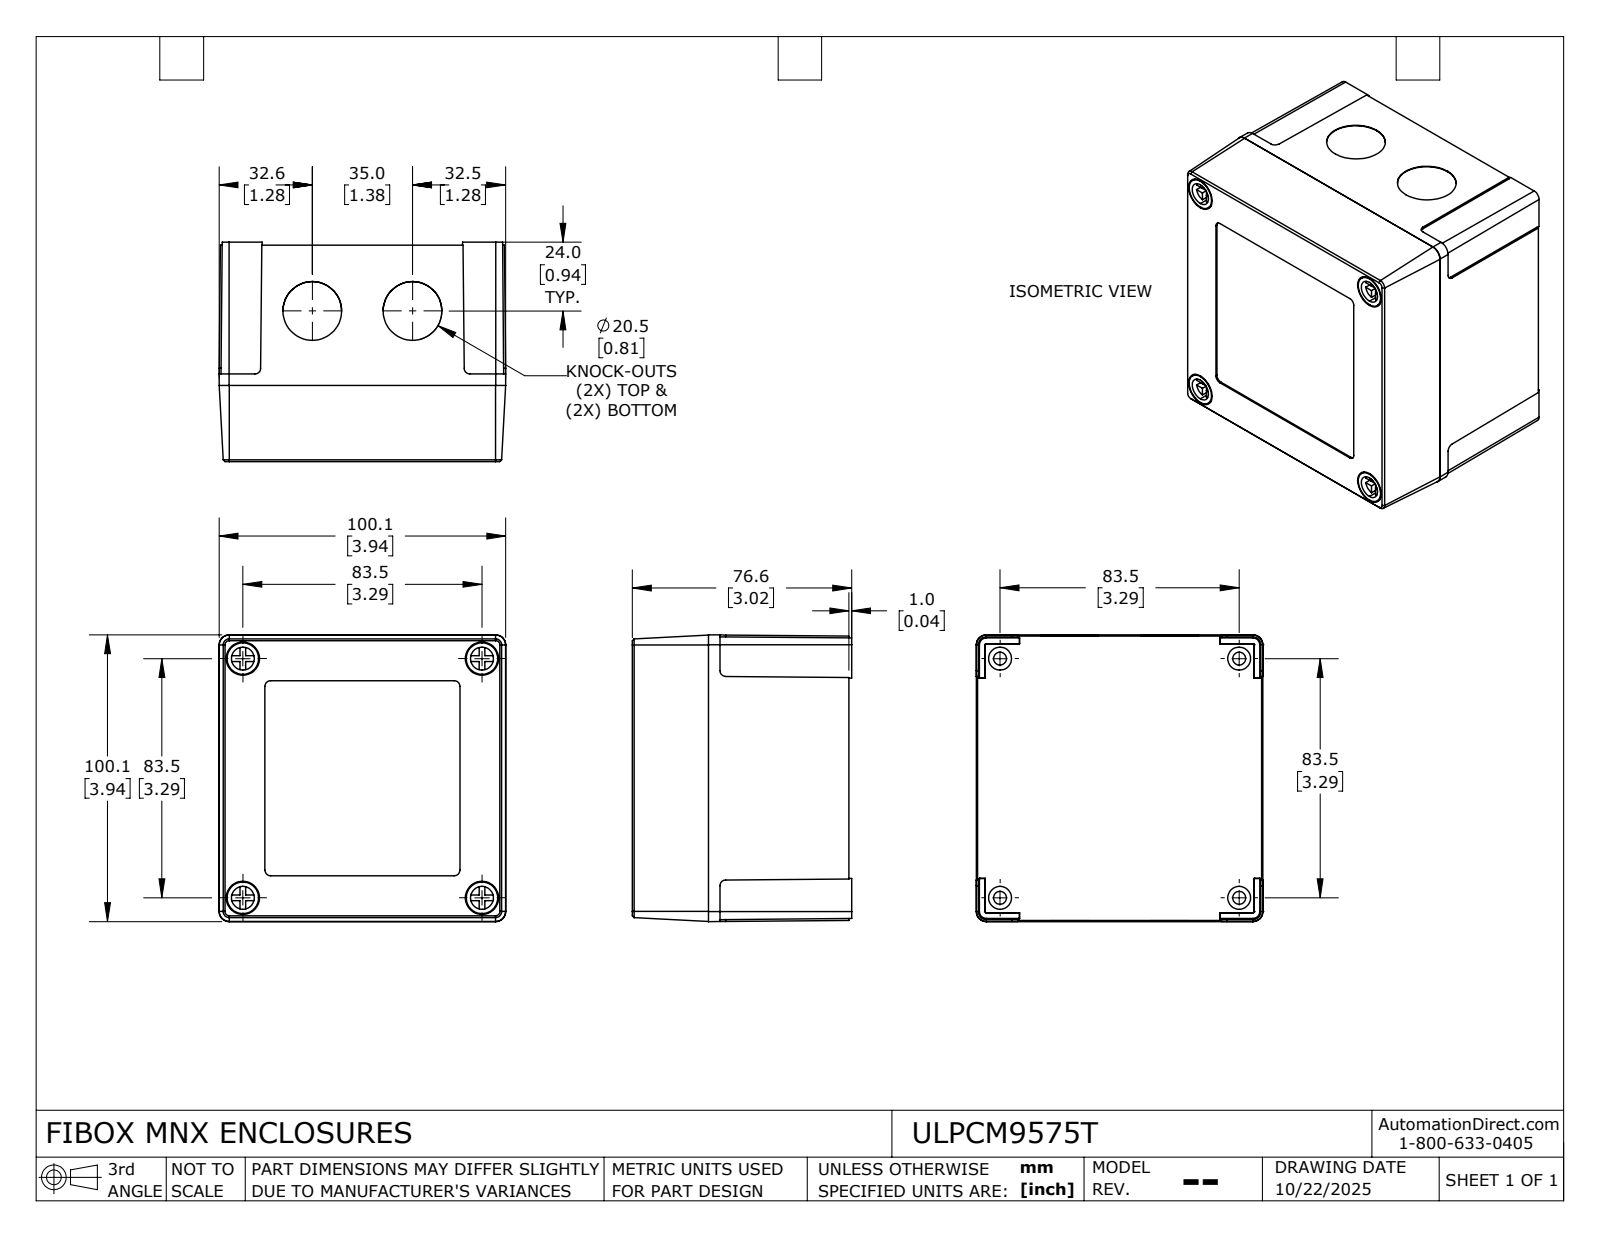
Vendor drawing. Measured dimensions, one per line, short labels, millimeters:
name: ULPCM9575T_Default
written by: SolidWorks 2024 (CONFIG_CONTROL_DESIGN)
unit: mm
bodies: 6 solids, 510 faces (294 planar, 176 cylindrical, 40 other)
size: 100.1 × 100.1 × 76.6
volume: 188 100 mm³; area: 109 500 mm²
holes: 6× ⌀2.4, 6× ⌀3, 6× ⌀3.2, 6× ⌀4, 4× ⌀4.5, 4× ⌀8, 4× ⌀11.6, 4× ⌀20.5
bosses: 6× ⌀8, 4× ⌀11, 4× ⌀7.2, 2× ⌀6
rounds: 8× R2, 6× R1.4, 4× R0.5, 4× R0.8, 4× R3, 4× R5, 2× R0.6
face distances: 4.2, 73.1, 3, 70.1, 2, 72.1, 75.1, 0.5, 72.6, 2.5
hole spacings: 20.4, 22.5, 29.4, 34.4, 37.1, 42.3, 46.3, 49
